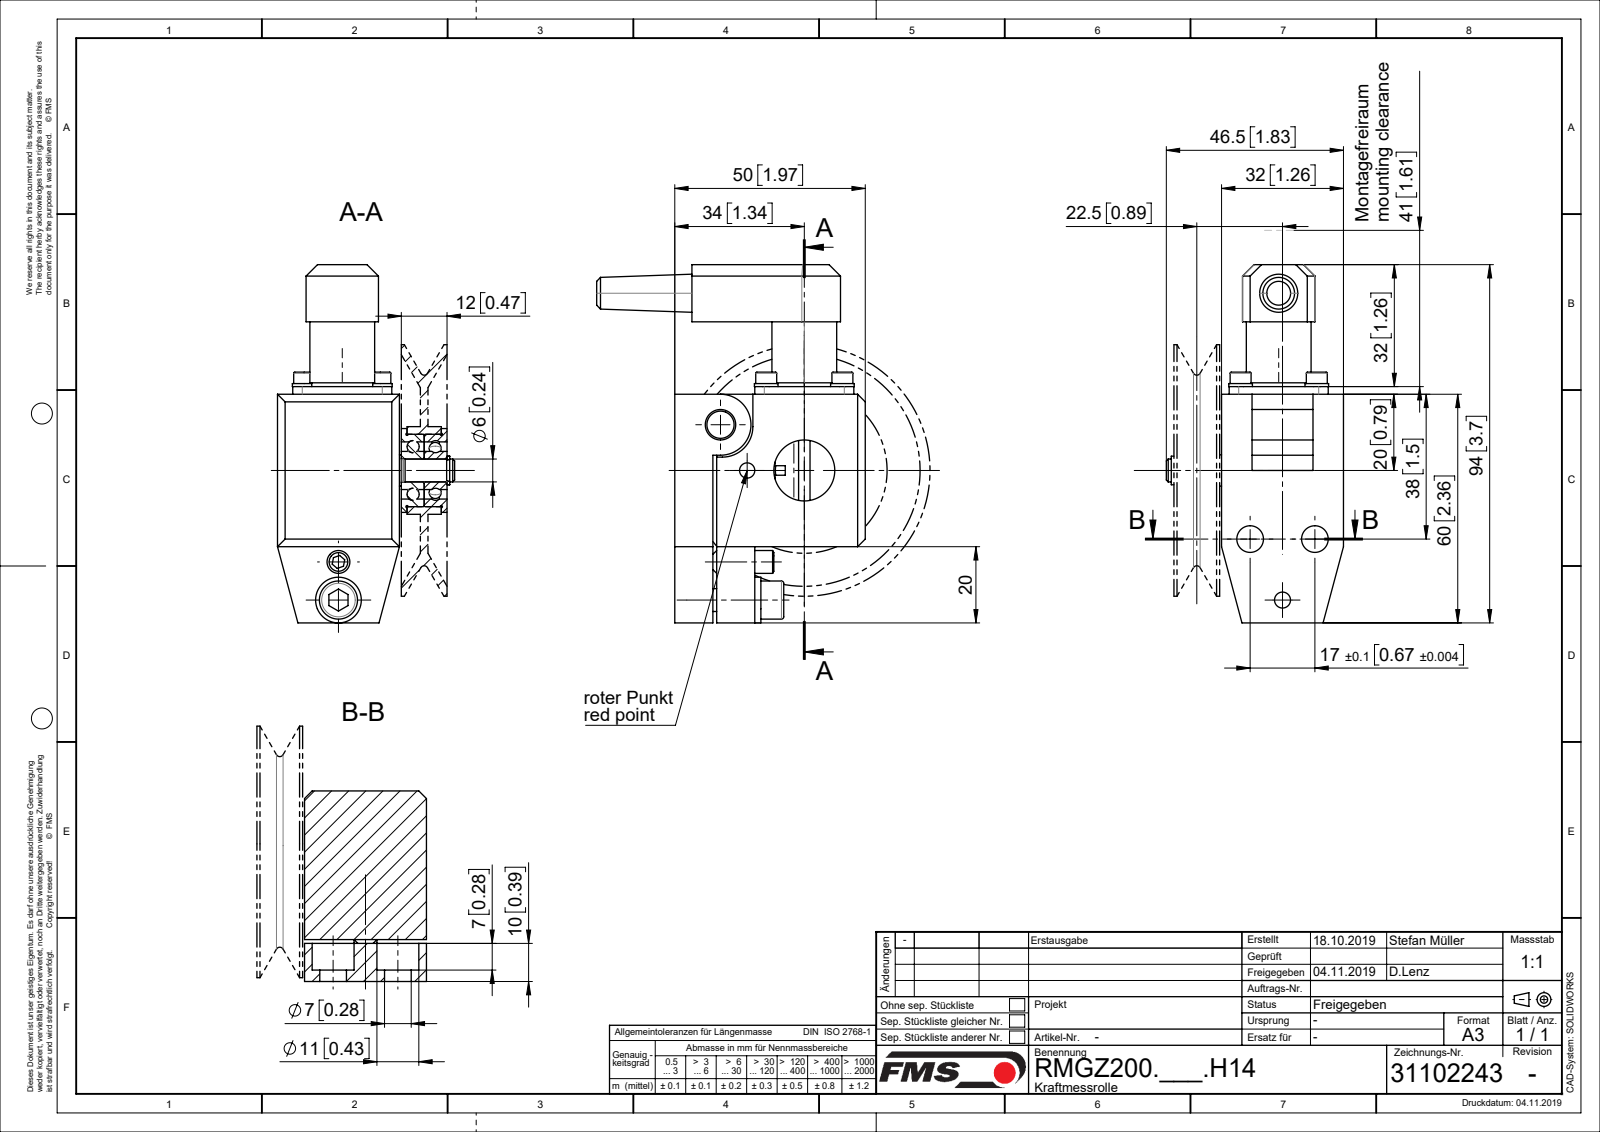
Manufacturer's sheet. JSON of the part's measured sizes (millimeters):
{"part_name": "ZEICHNUNG4; R1302201; R1206234(1); R1206234 (+8 more)", "step_written_by": "Mechanical Desktop 2009 (CONFIG_CONTROL_DESIGN)", "units": "millimeters", "bodies": {"solids": 22, "faces": 511, "planar": 152, "cylindrical": 201, "other": 158}, "overall_size": [93, 87.5, 46.5], "volume_mm3": 95472, "surface_area_mm2": 47750, "round_holes": [[2, 5], [2.6, 4], [3.2, 4], [6, 2], [7, 2], [11, 2], [15, 2], [16, 2], [4, 1], [4.33, 1], [5.15, 1], [5.3, 1]], "round_bosses_or_shafts": [[1.5, 5], [6.2, 4], [5.5, 4], [3, 4], [10, 2], [66, 1], [23, 1], [22, 1]], "partial_cylinders_radius": [[2.5, 4], [8, 2], [9.5, 1]], "face_to_face_distances": [10, 11, 2, 40, 5, 1, 32, 7, 5.5, 8], "hole_center_spacings": [14.14, 20, 3, 3.14, 3.65, 3.96, 6, 6.34]}
